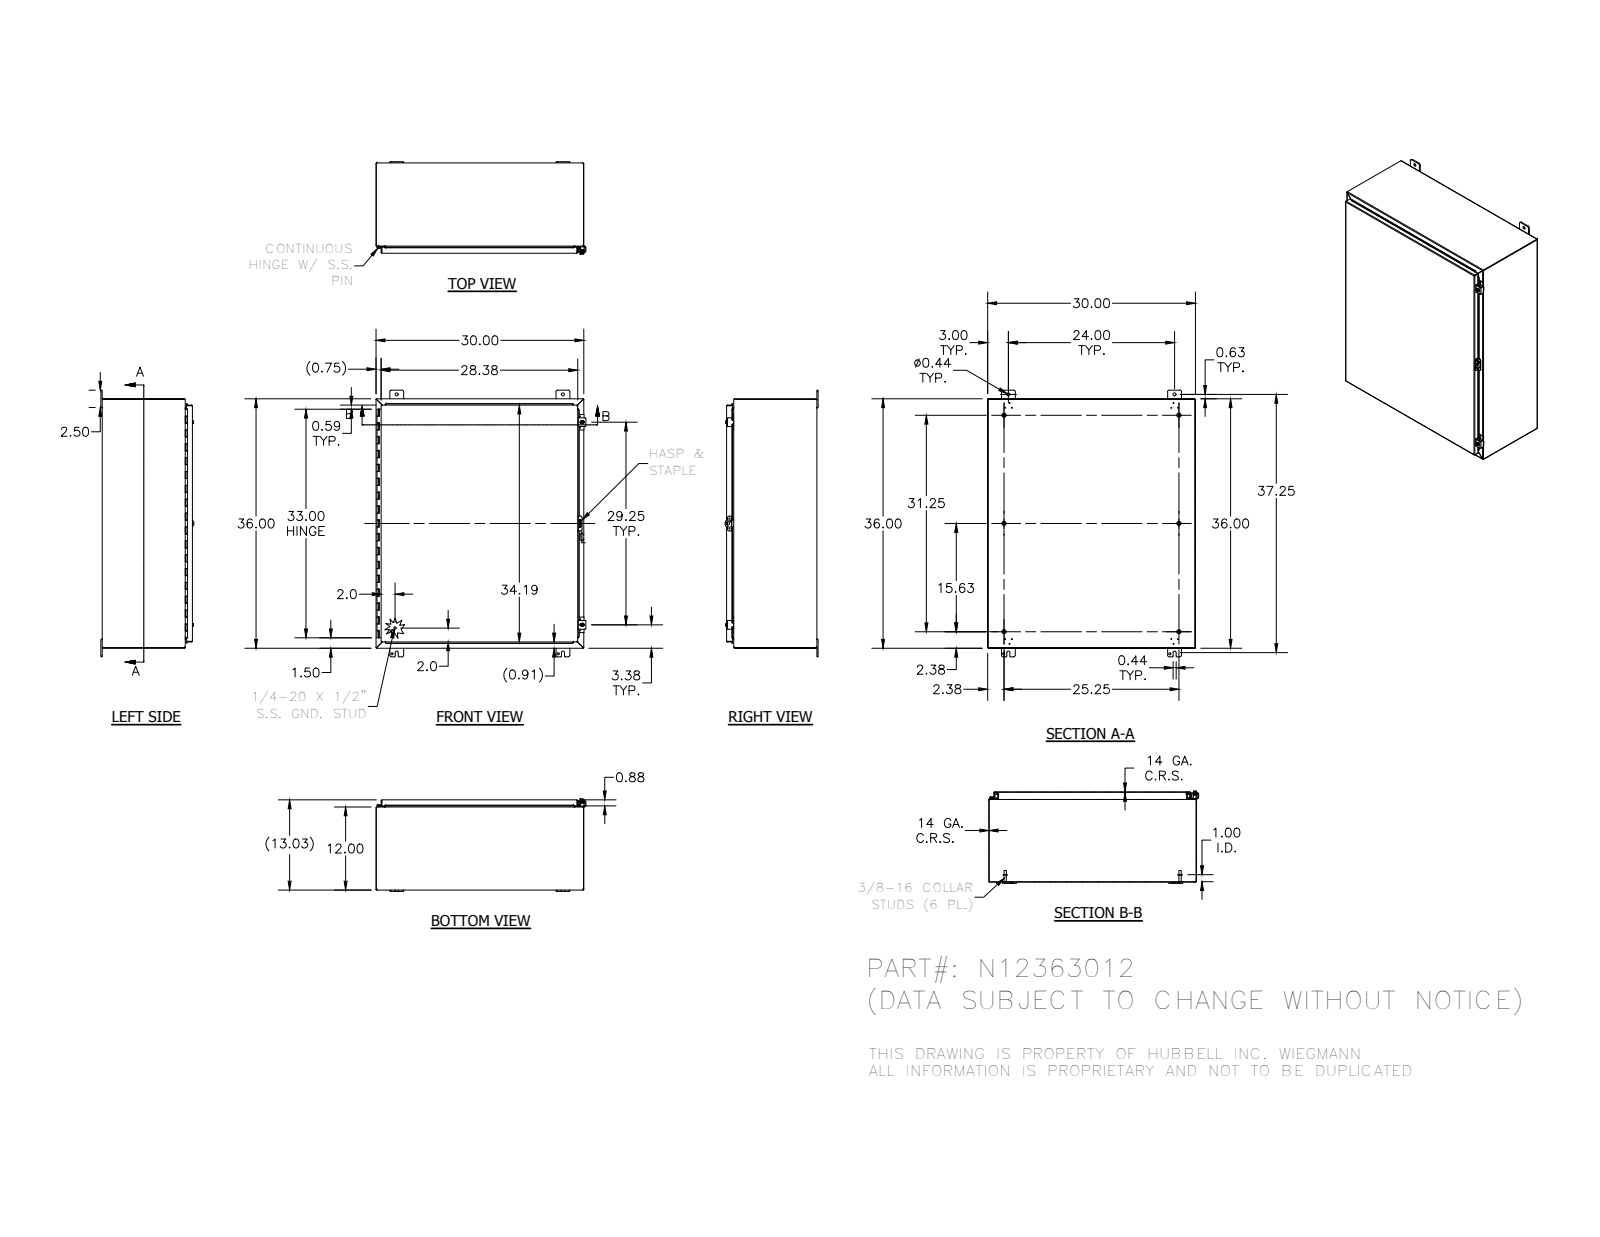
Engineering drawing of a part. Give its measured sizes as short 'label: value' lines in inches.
name: N12363012; 34840; 38420; N12363012BKP (+8 more)
written by: Autodesk Inventor 2012 (AUTOMOTIVE_DESIGN)
unit: in
bodies: 29 solids, 1100 faces (607 planar, 374 cylindrical, 119 other)
size: 38.5 × 30.311 × 13.41
volume: 320.1 in³; area: 8 452 in²
holes: 12× ⌀0.12, 7× ⌀0.11, 4× ⌀0.313, 4× ⌀0.438, 2× ⌀0.211, 2× ⌀0.281, 2× ⌀0.3, 1× ⌀0.125, 1× ⌀0.156, 1× ⌀0.5
bosses: 6× ⌀0.625, 6× ⌀0.33, 4× ⌀0.25, 2× ⌀0.52, 2× ⌀0.5, 2× ⌀0.35, 2× ⌀0.115, 1× ⌀0.337
rounds: 27× R0.03, 25× R0.063, 25× R0.125, 25× R0.25, 23× R0.031, 23× R0.105, 8× R0.07, 4× R0.1
face distances: 0.074, 12.959, 12.885, 13.033, 29.926, 35.926, 29.852, 30, 36, 35.852
hole spacings: 24, 0.759, 0.94, 0.969, 1.995, 23.367, 24.335, 33.38
